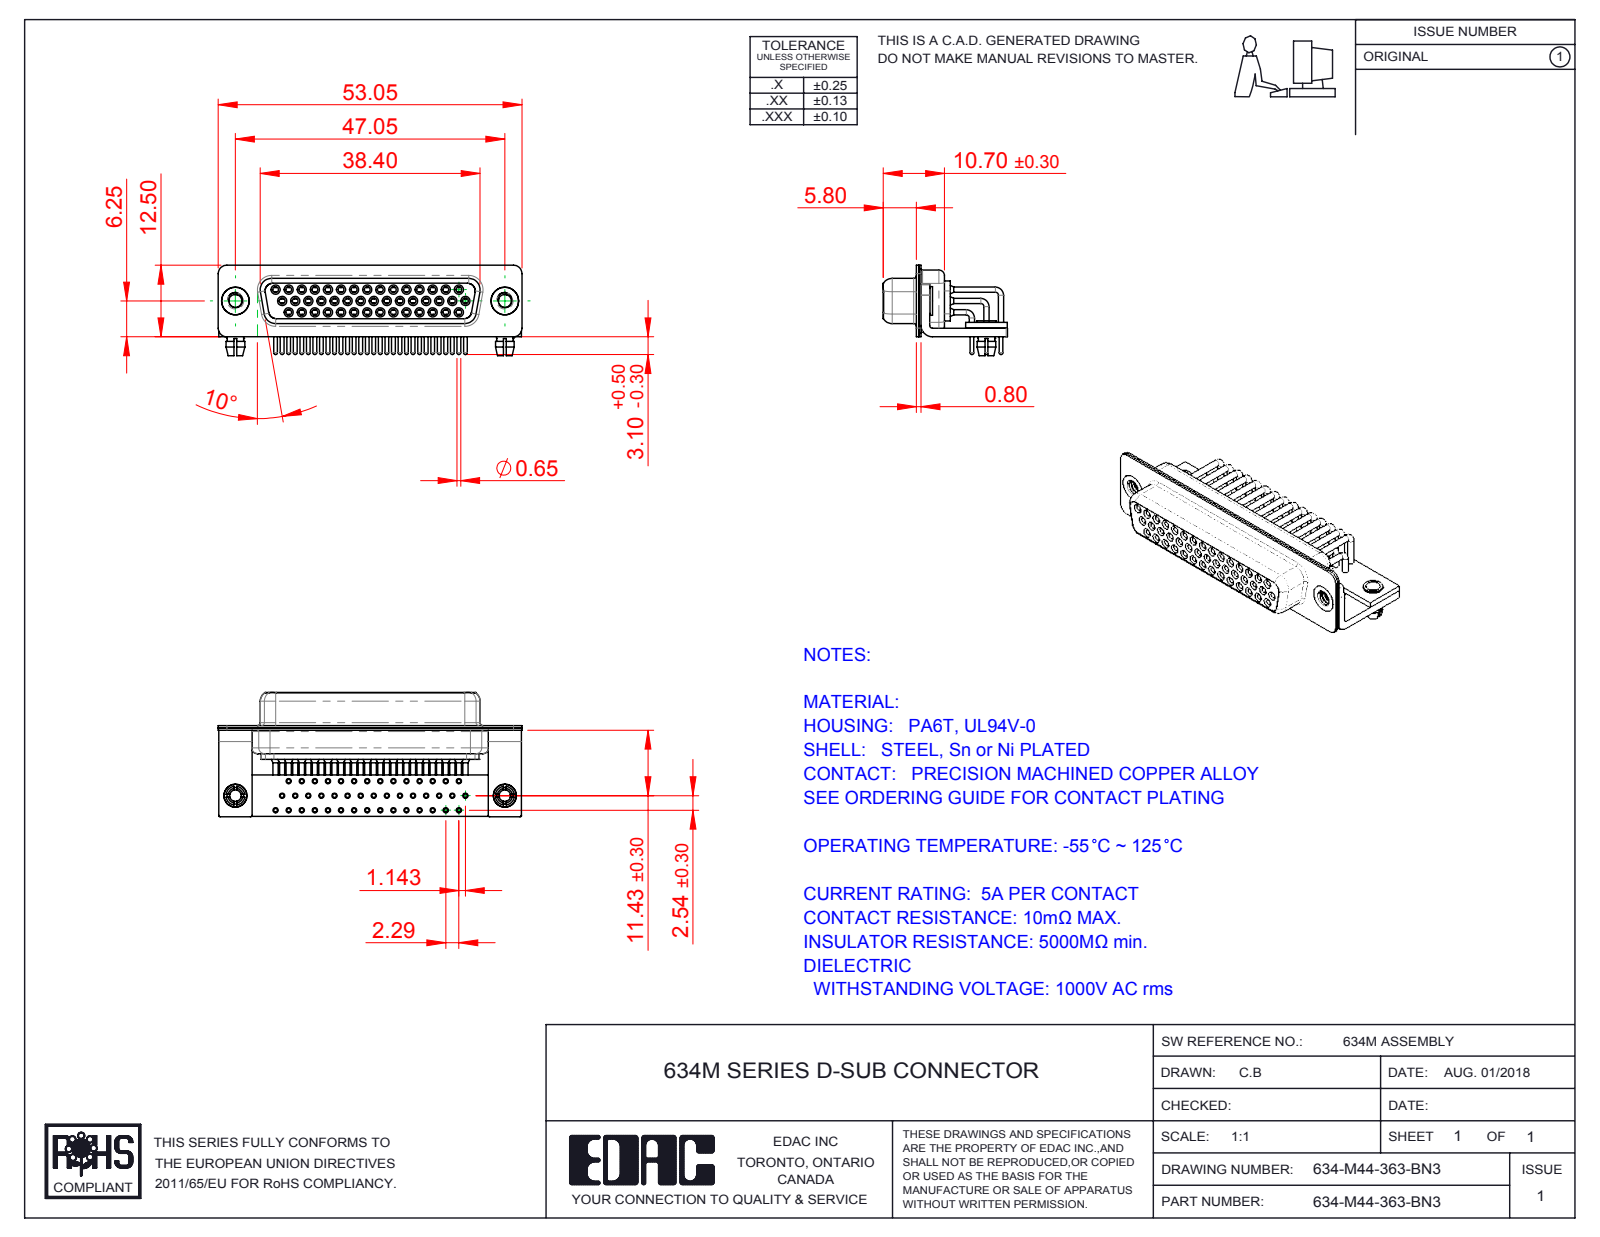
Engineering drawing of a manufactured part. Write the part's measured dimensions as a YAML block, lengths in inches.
part_name: "634M Stabilizer Bracket; 634M Contact Row 1; 634M Shell Rear_44 Contacts; 634M Housing_44 Contacts (+7 more)"
step_written_by: "SolidWorks 2016 (CONFIG_CONTROL_DESIGN)"
units: inches
bodies: {solids: 54, faces: 2841, planar: 801, cylindrical: 1291, other: 749}
overall_size: [2.089, 0.854, 0.622]
volume: 0.275
surface_area: 23
round_holes:
  - {diameter: 0.079, count: 46}
  - {diameter: 0.035, count: 44}
  - {diameter: 0.039, count: 44}
  - {diameter: 0.043, count: 44}
  - {diameter: 0.067, count: 44}
  - {diameter: 0.071, count: 44}
  - {diameter: 0.089, count: 2}
  - {diameter: 0.098, count: 2}
  - {diameter: 0.126, count: 2}
  - {diameter: 0.157, count: 2}
  - {diameter: 0.189, count: 2}
round_bosses_or_shafts:
  - {diameter: 0.063, count: 44}
  - {diameter: 0.059, count: 44}
  - {diameter: 0.035, count: 44}
  - {diameter: 0.026, count: 44}
  - {diameter: 0.197, count: 2}
  - {diameter: 0.193, count: 2}
  - {diameter: 0.157, count: 2}
  - {diameter: 0.134, count: 2}
partial_cylinders:
  - {radius: 0.01, count: 16}
  - {radius: 0.059, count: 16}
  - {radius: 0.079, count: 13}
  - {radius: 0.053, count: 8}
  - {radius: 0.063, count: 8}
  - {radius: 0.02, count: 5}
  - {radius: 0.024, count: 4}
  - {radius: 0.026, count: 4}
face_to_face_distances: [0.016, 0.091, 0.039, 0.075, 0.031, 0.368, 0.057, 0.352, 0.059, 0.033]
hole_center_spacings: [0.09, 0.09, 0.18, 0.27, 0.45, 0.156, 0.324, 0.36]
